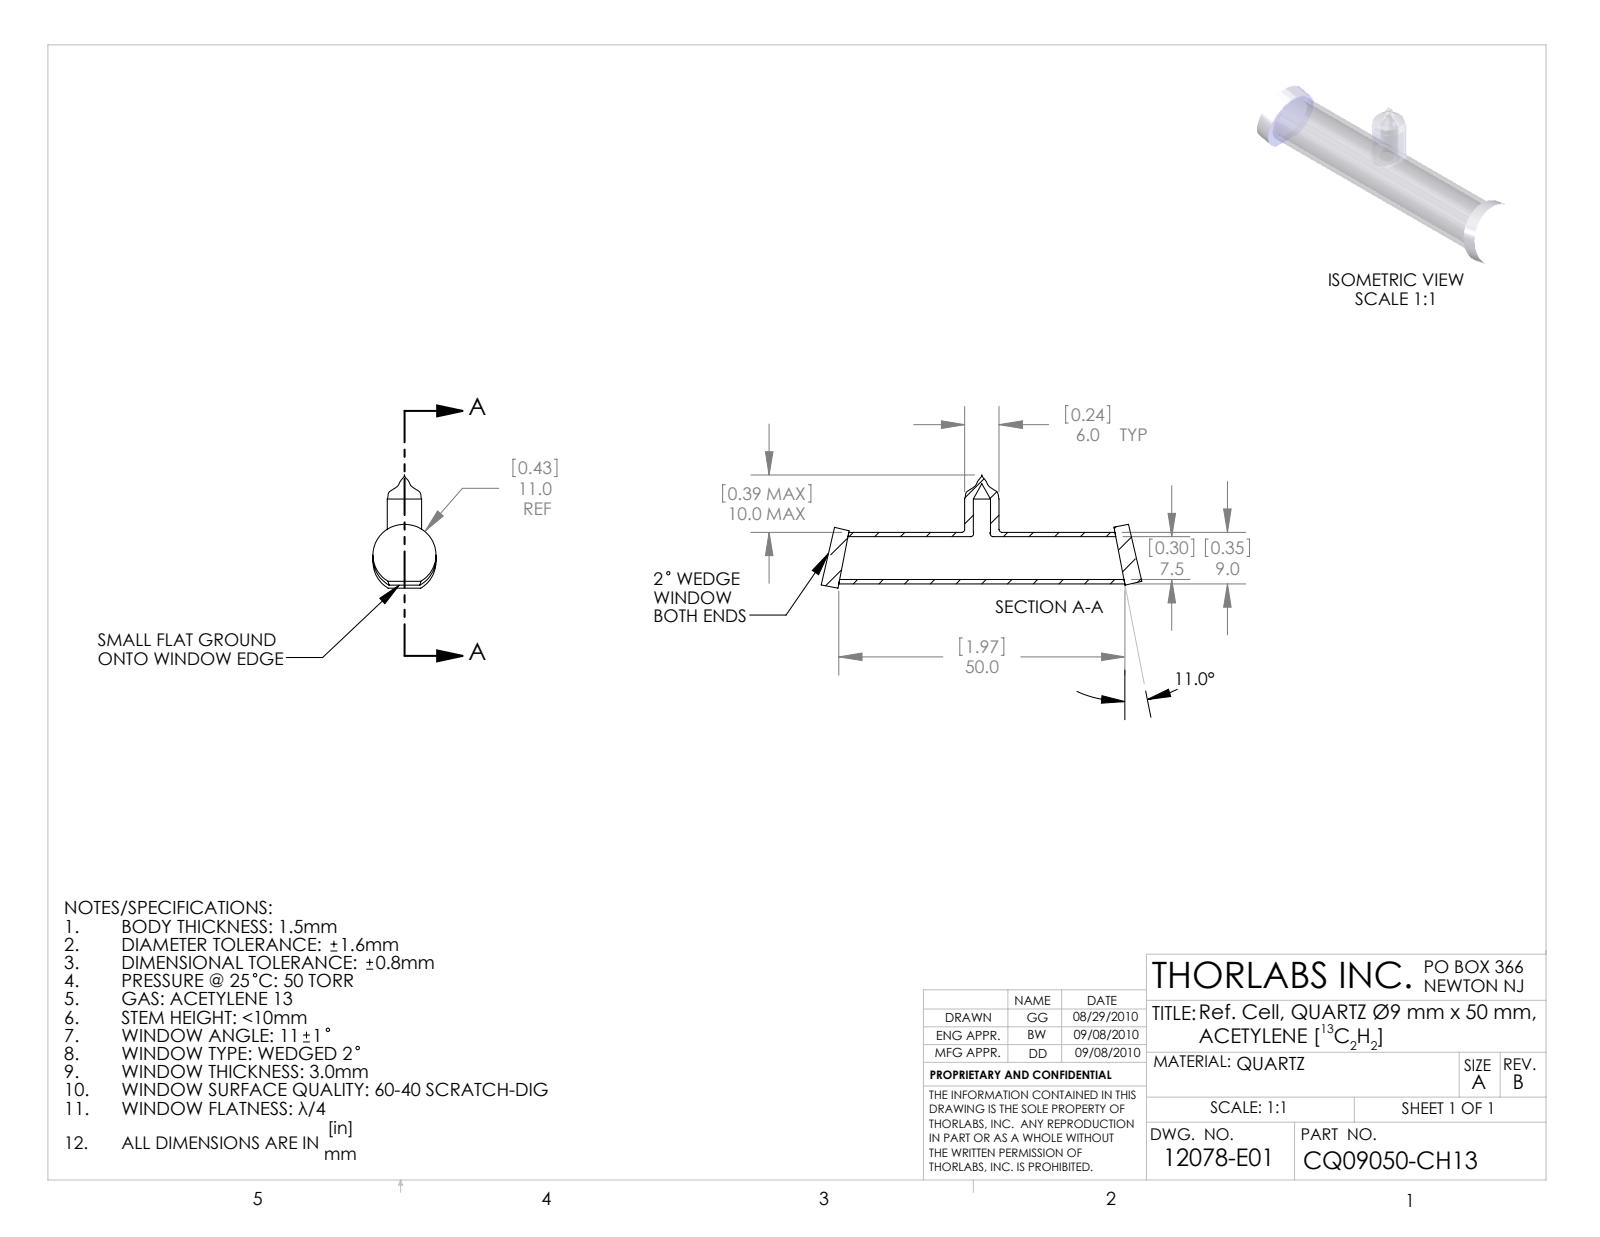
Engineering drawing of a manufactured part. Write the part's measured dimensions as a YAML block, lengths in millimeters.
part_name: "12078-E0W"
step_written_by: "SolidWorks 2009 (AUTOMOTIVE_DESIGN)"
units: millimeters
bodies: {solids: 3, faces: 33, planar: 8, cylindrical: 17, other: 8}
overall_size: [55.95, 19.74, 11]
volume: 1620
surface_area: 3311
round_holes:
  - {diameter: 2.91, count: 1}
  - {diameter: 3, count: 1}
  - {diameter: 7.5, count: 1}
round_bosses_or_shafts:
  - {diameter: 11, count: 2}
  - {diameter: 9, count: 1}
  - {diameter: 6, count: 1}
